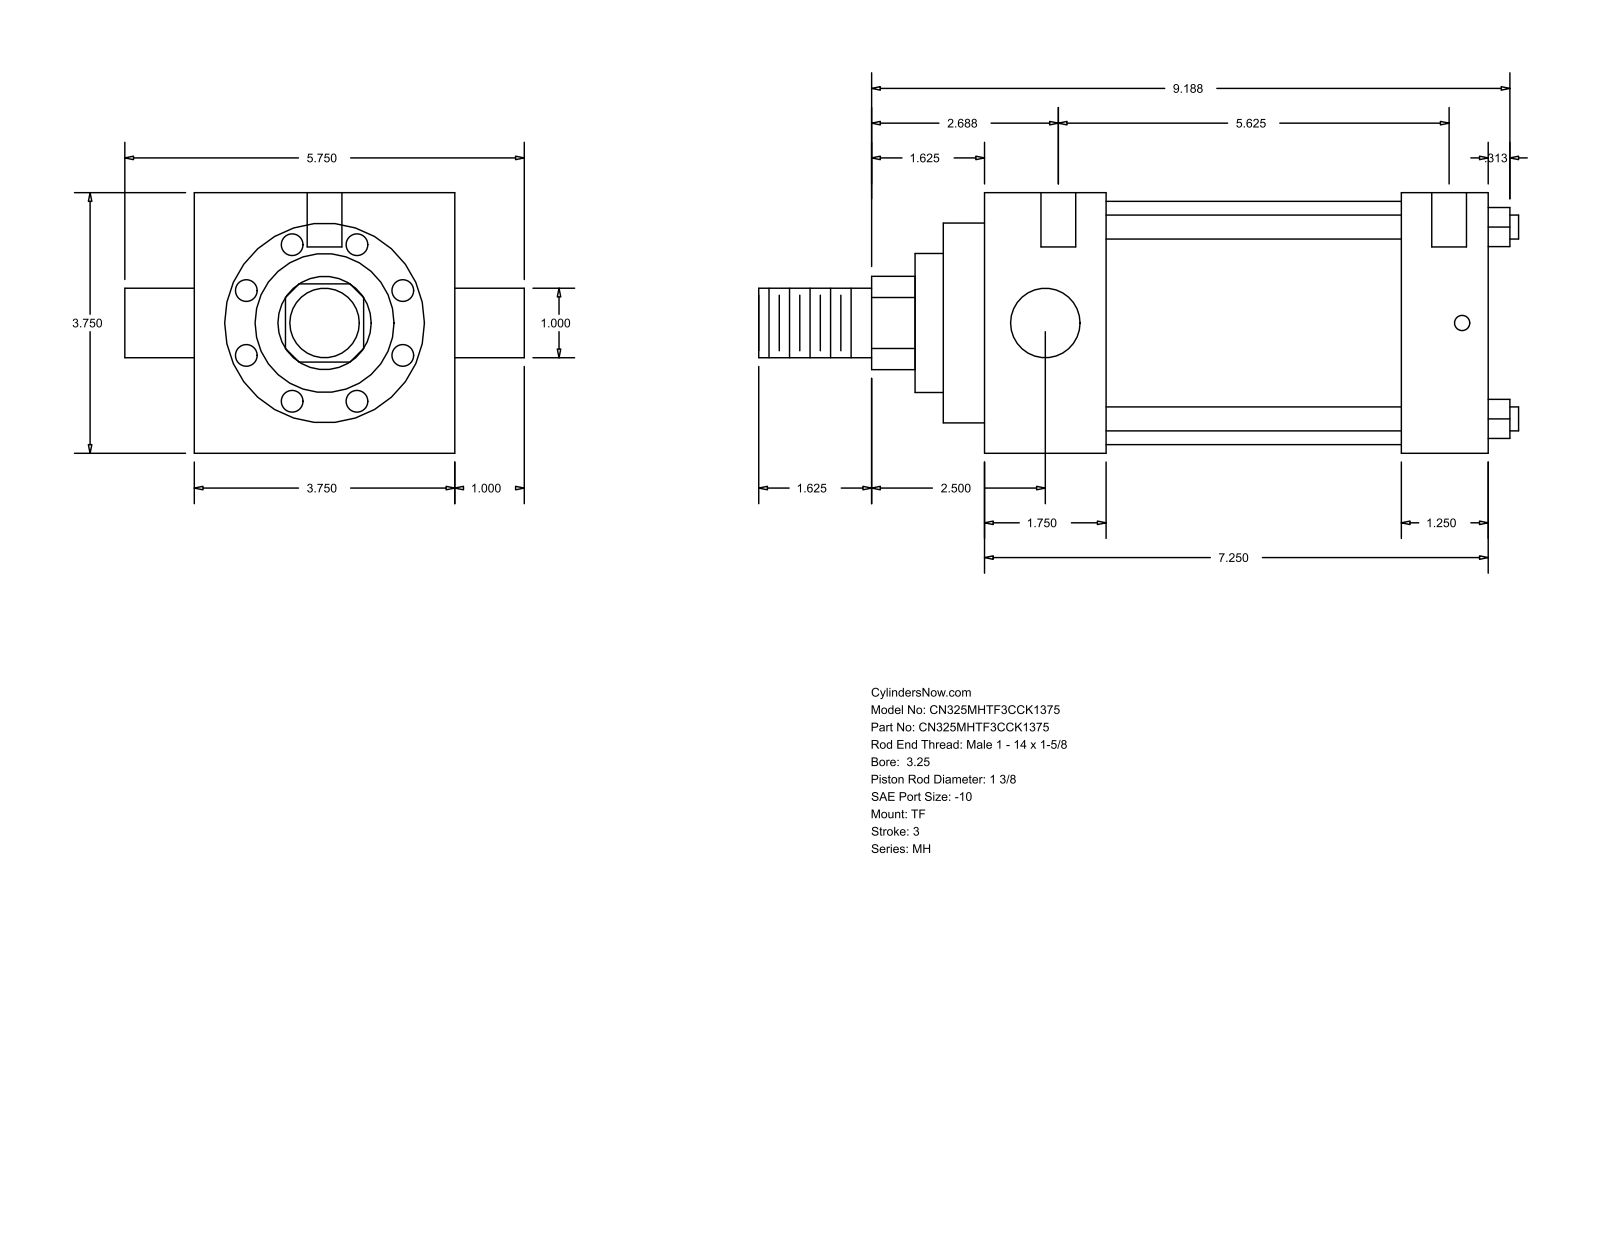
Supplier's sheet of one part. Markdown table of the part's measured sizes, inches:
| quantity | value |
| --- | --- |
| part name | MH_TF__0325_1.375 |
| STEP written by | GSSL Pune (CONFIG_CONTROL_DESIGN) |
| units | inches |
| bodies | 0 solids, 86 faces (61 planar, 25 cylindrical, 0 other) |
| overall size | 10.937 × 5.75 × 3.75 |
| round holes (diameter × count) | 0.219 × 3, 0.5 × 2 |
| round bosses / shafts (diameter × count) | 0.345 × 4, 1 × 2, 3.5 × 1, 2.875 × 1, 2 × 1, 1.375 × 1 |
| partial cylindrical surfaces (radius × count) | 0.672 × 1 |
| main face-to-face distances | 3.75, 7.25, 1.75, 6, 4.25, 5.5, 1.25, 0.594, 2.344, 6.594 |
| hole center spacings | 0.063, 0.187, 5.625, 5.688, 5.813, 5.875 |
